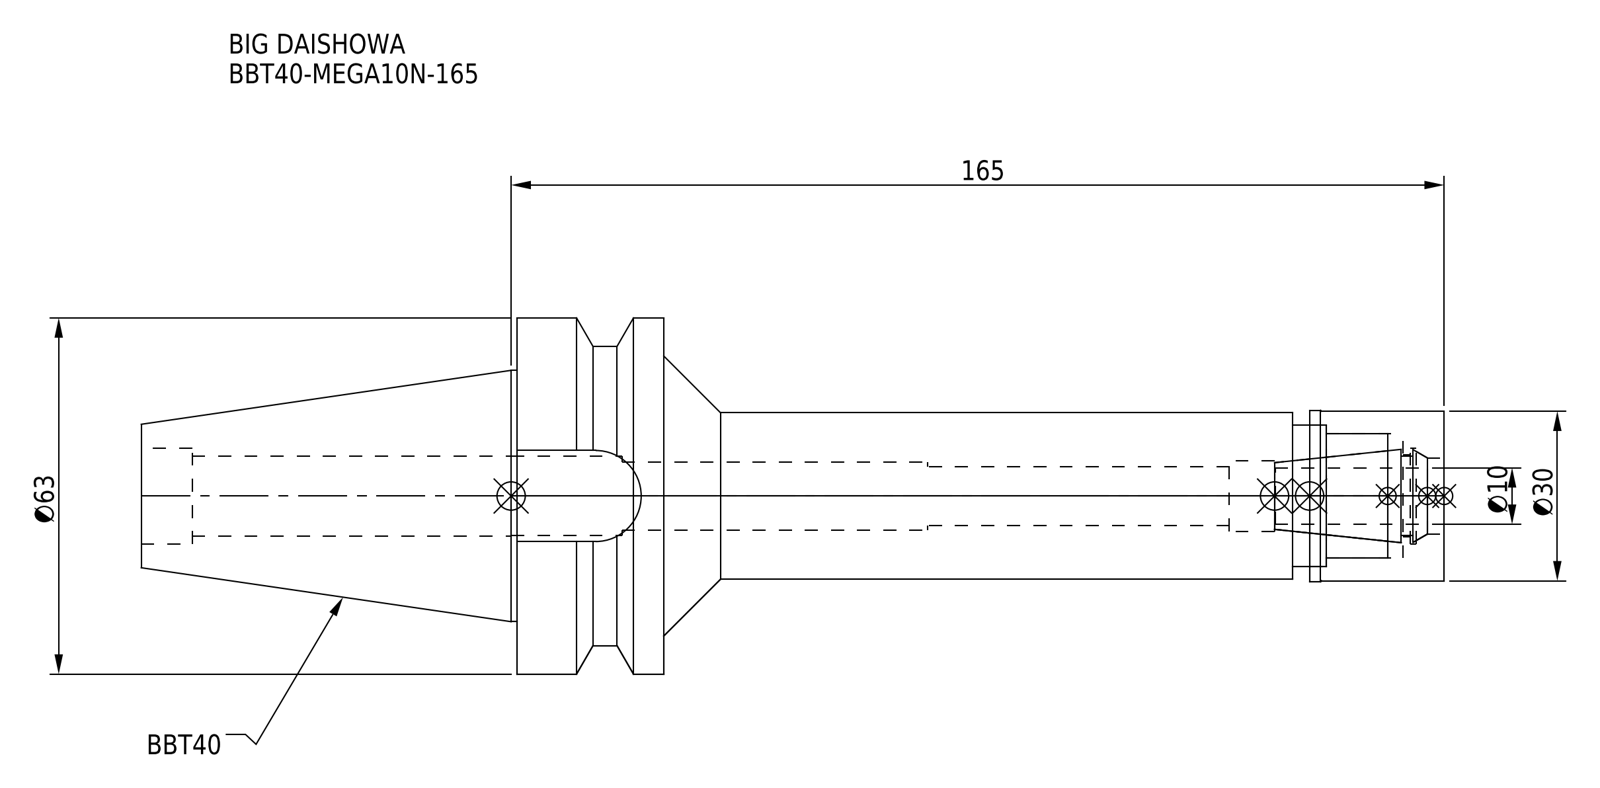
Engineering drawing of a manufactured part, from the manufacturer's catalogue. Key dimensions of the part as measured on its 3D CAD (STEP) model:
Part name (STEP PRODUCT): BBT40MN10165-100_ASM.stp; BBT40-MEGA10N-165_1.stp; BBT40-MEGA10N-165; BBT40-MEGA10N-165-100.stp (+3 more)
STEP written by: SolidWorks 2019 (CONFIG_CONTROL_DESIGN)
Units: millimetres
Bodies: 2 solids, 80 faces (24 planar, 42 cylindrical, 14 other)
Overall size (bounding box): 230.4 × 63 × 63
Volume: 204 680 mm³ · Surface area: 43 495 mm²
Round holes (diameter × count): ⌀10.4 ×1, ⌀12 ×1, ⌀12.5 ×1, ⌀13.5 ×1, ⌀14 ×1, ⌀14.2 ×1, ⌀14.5 ×1, ⌀17 ×1, ⌀22 ×1, ⌀25 ×1
Round bosses / shafts (diameter × count): ⌀63 ×1, ⌀53 ×1, ⌀44.45 ×1, ⌀30.3 ×1, ⌀30 ×1, ⌀29.5 ×1
Partial cylindrical surfaces — rounded edges, fillets, slot ends (radius × count): R8.05 ×1
Main face-to-face distances: 26, 138, 164, 45, 230.4, 92.4, 66.4, 23.8, 114.2, 140.2
